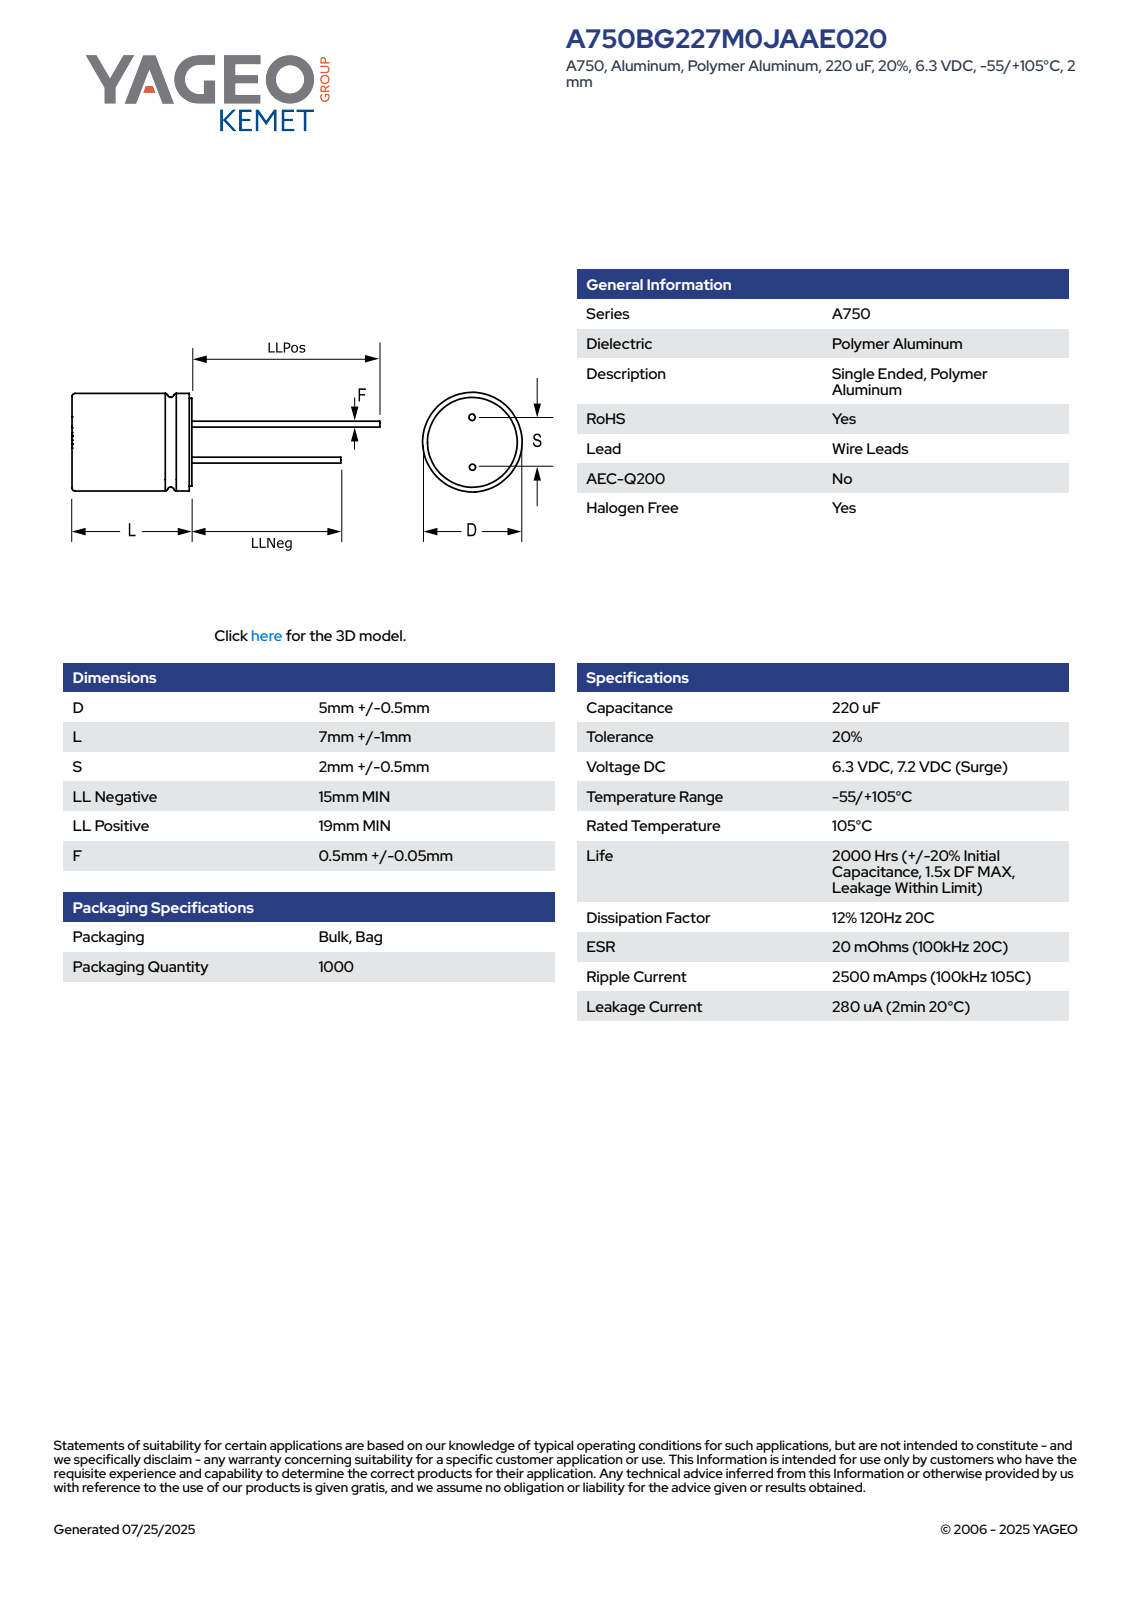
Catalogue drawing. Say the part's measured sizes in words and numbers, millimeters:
The part is named "CAR_KP_5X7_D5.5L8S2F0.55". Its 3-D file was written by "SolidWorks 2014 (AUTOMOTIVE_DESIGN)". It is 4 solids with 75 faces: 61 planar, 8 cylindrical and 6 other. Overall it measures 27 by 5.5 by 5.5 millimeters. Its volume is 196 cubic millimeters and its surface area 249 square millimeters. Round bosses or shafts: 2 of diameter 0.55, 1 of diameter 5.5. The main face-to-face distances are 8, 8.01, 23.01, 27.01, 23, 27, 15, 19, 4, 0.6.
